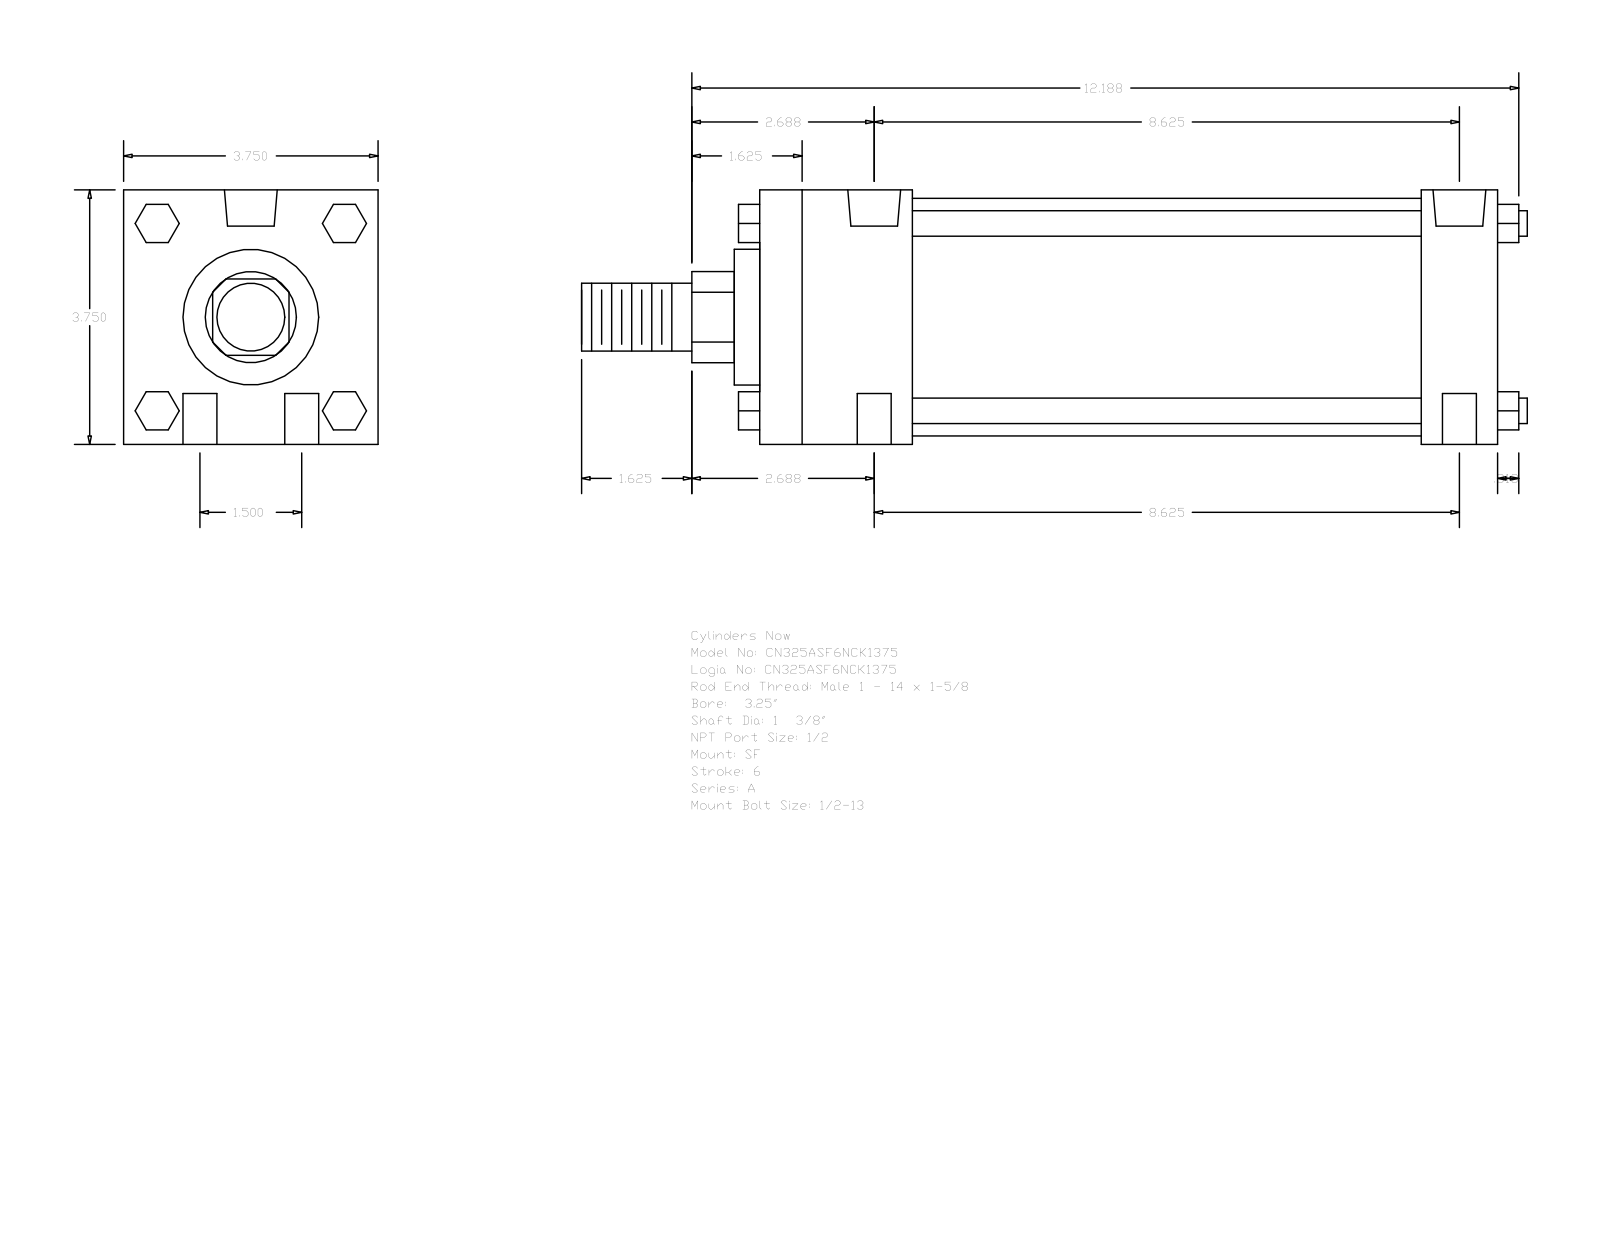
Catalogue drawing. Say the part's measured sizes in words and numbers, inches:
The part is named "A_SF__0325_1.375". Its 3-D file was written by "GSSL Pune (CONFIG_CONTROL_DESIGN)". It is 0 solids with 124 faces: 94 planar, 30 cylindrical and 0 other. Overall it measures 13.937 by 3.75 by 3.75 inches. Round holes: 4 of diameter 0.5, 2 of diameter 0.344, 2 of diameter 0.778. Round bosses or shafts: 4 of diameter 0.375, 1 of diameter 3.5, 1 of diameter 2, 1 of diameter 1.375, 1 of diameter 1. Partial cylindrical surfaces (rounded edges, fillets, slot ends): 1 of radius 0.672. The main face-to-face distances are 3.75, 10.875, 2.25, 9.75, 1.125, 7.5, 8.625, 2.625, 0.375, 10.125. The hole center spacings are 0.75, 8.658, 8.625, 1.5, 8.755, 8.375.
